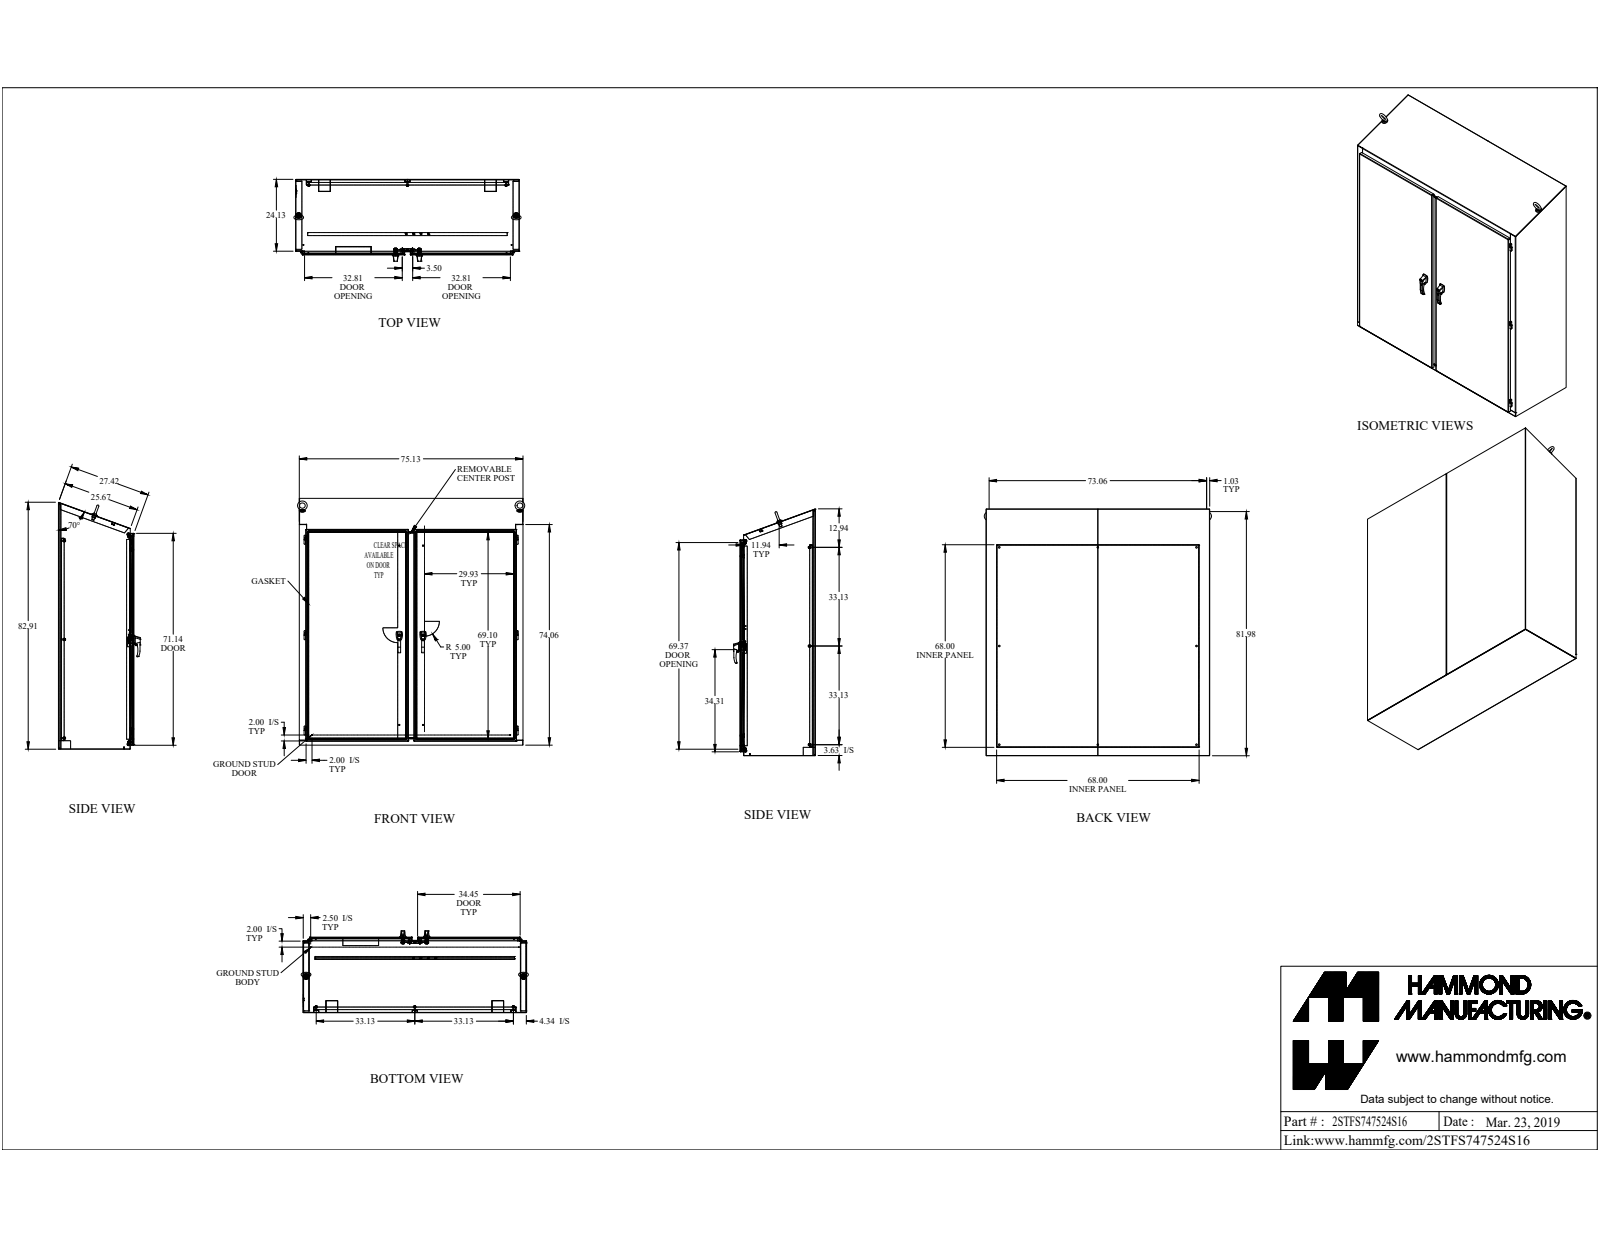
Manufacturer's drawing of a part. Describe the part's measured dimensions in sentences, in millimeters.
The part is named "2STFS747524S16". Its 3-D file was written by "SolidWorks 2019 (CONFIG_CONTROL_DESIGN)". It is 146 solids with 2404 faces: 1417 planar, 729 cylindrical and 258 other. Overall it measures 2104.6 by 1938.2 by 698.3 millimeters. Its volume is 46 260 000 cubic millimeters and its surface area 36 380 000 square millimeters. Round holes: 8 of diameter 7.8, 8 of diameter 8.9, 8 of diameter 14.3, 7 of diameter 6.4, 6 of diameter 7.1, 6 of diameter 8, 6 of diameter 11.3, 4 of diameter 5, 4 of diameter 6.5, 4 of diameter 7.1, 4 of diameter 9.9, 4 of diameter 10.5. Round bosses or shafts: 12 of diameter 25.4, 8 of diameter 16.5, 8 of diameter 9.5, 8 of diameter 8.4, 4 of diameter 19.1, 4 of diameter 16, 4 of diameter 15.9, 4 of diameter 11.2. Partial cylindrical surfaces (rounded edges, fillets, slot ends): 47 of radius 3.2, 33 of radius 12.7, 32 of radius 0.5, 30 of radius 1.2, 30 of radius 3.6, 20 of radius 1.5, 16 of radius 6.4, 12 of radius 0.8. The main face-to-face distances are 2.4, 2.4, 639.7, 642.1, 642.1, 644.6, 3.2, 596.1, 593.7, 46. The hole center spacings are 1855.7, 202.8, 1881.4, 1682.8, 28.6, 32.7, 189.1, 204.8.
